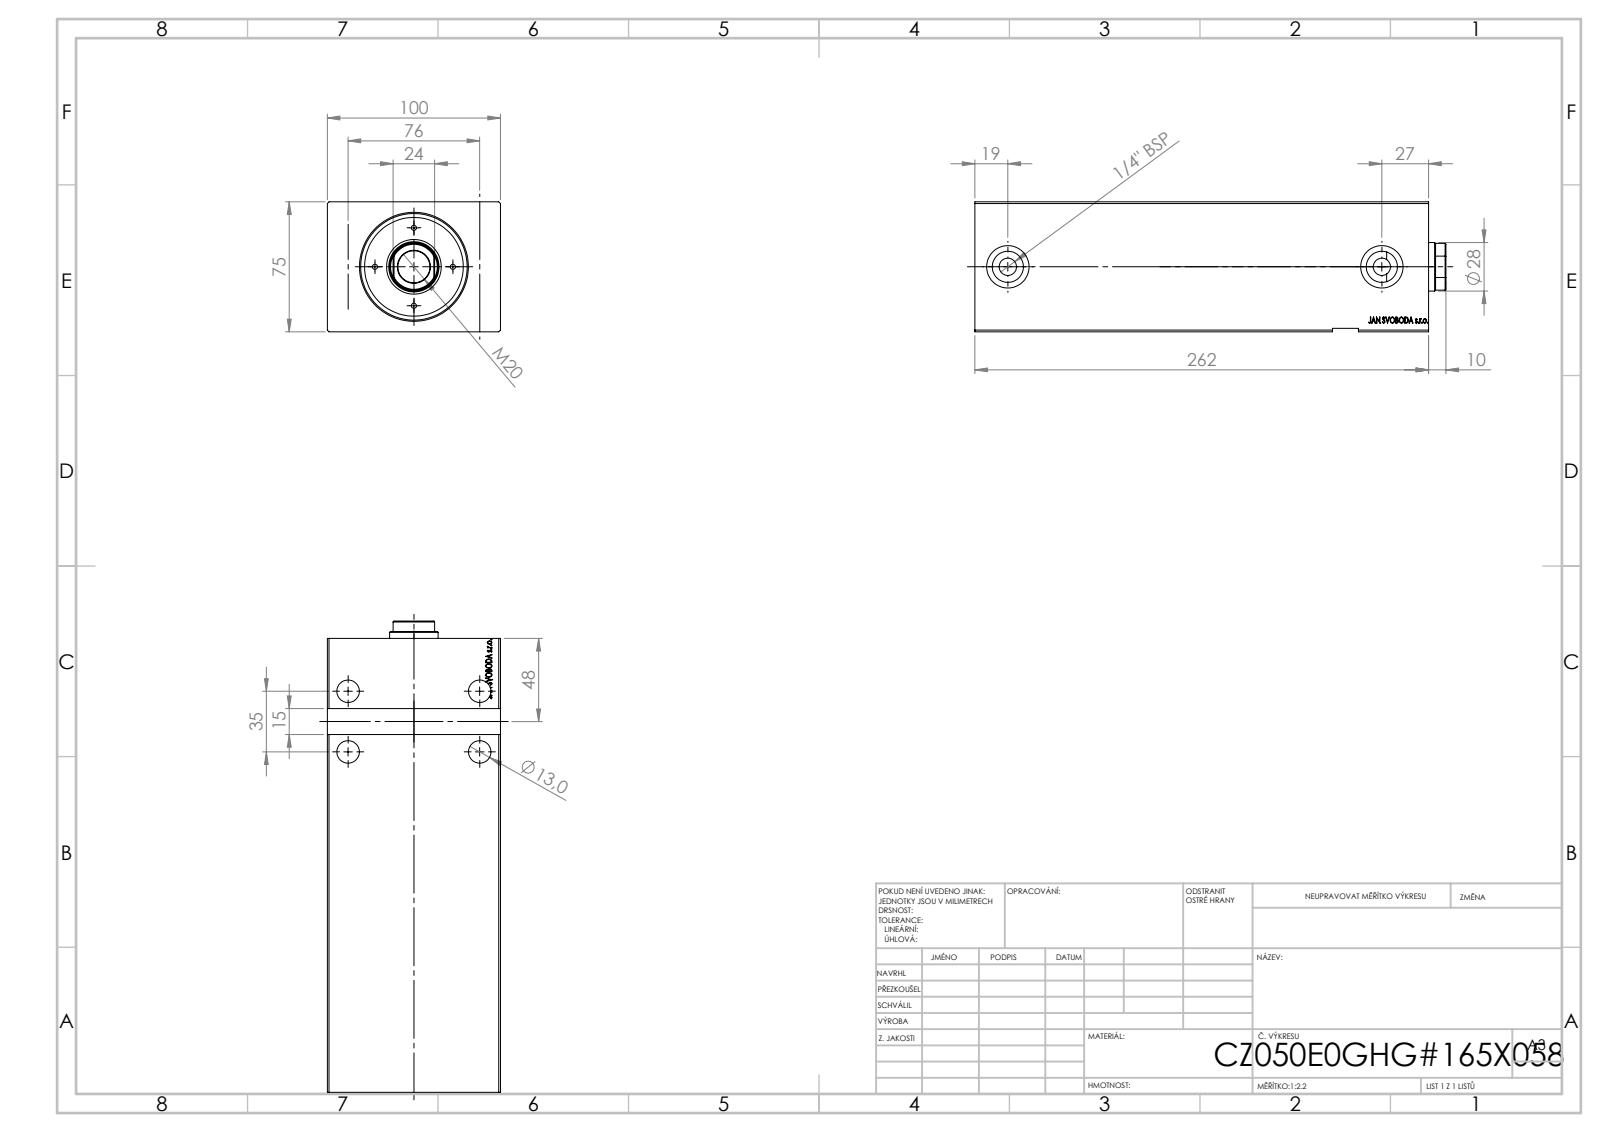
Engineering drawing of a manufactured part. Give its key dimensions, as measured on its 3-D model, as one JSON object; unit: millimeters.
{"step_written_by": "SolidWorks 2019 (CONFIG_CONTROL_DESIGN)", "units": "millimeters", "bodies": {"solids": 1, "faces": 776, "planar": 375, "cylindrical": 31, "other": 370}, "overall_size": [262, 100, 75], "volume_mm3": 1425000, "surface_area_mm2": 157690, "round_holes": [[13, 4], [8, 2], [10, 2], [18, 2], [24.5, 2], [36, 1], [50, 1], [61.5, 1]], "face_to_face_distances": [75, 100, 262, 244.2, 17.8, 2, 73, 261.8, 17.6, 10], "hole_center_spacings": [35, 76, 83.67, 21.03, 34.82, 56.38, 62.84, 168.69]}
